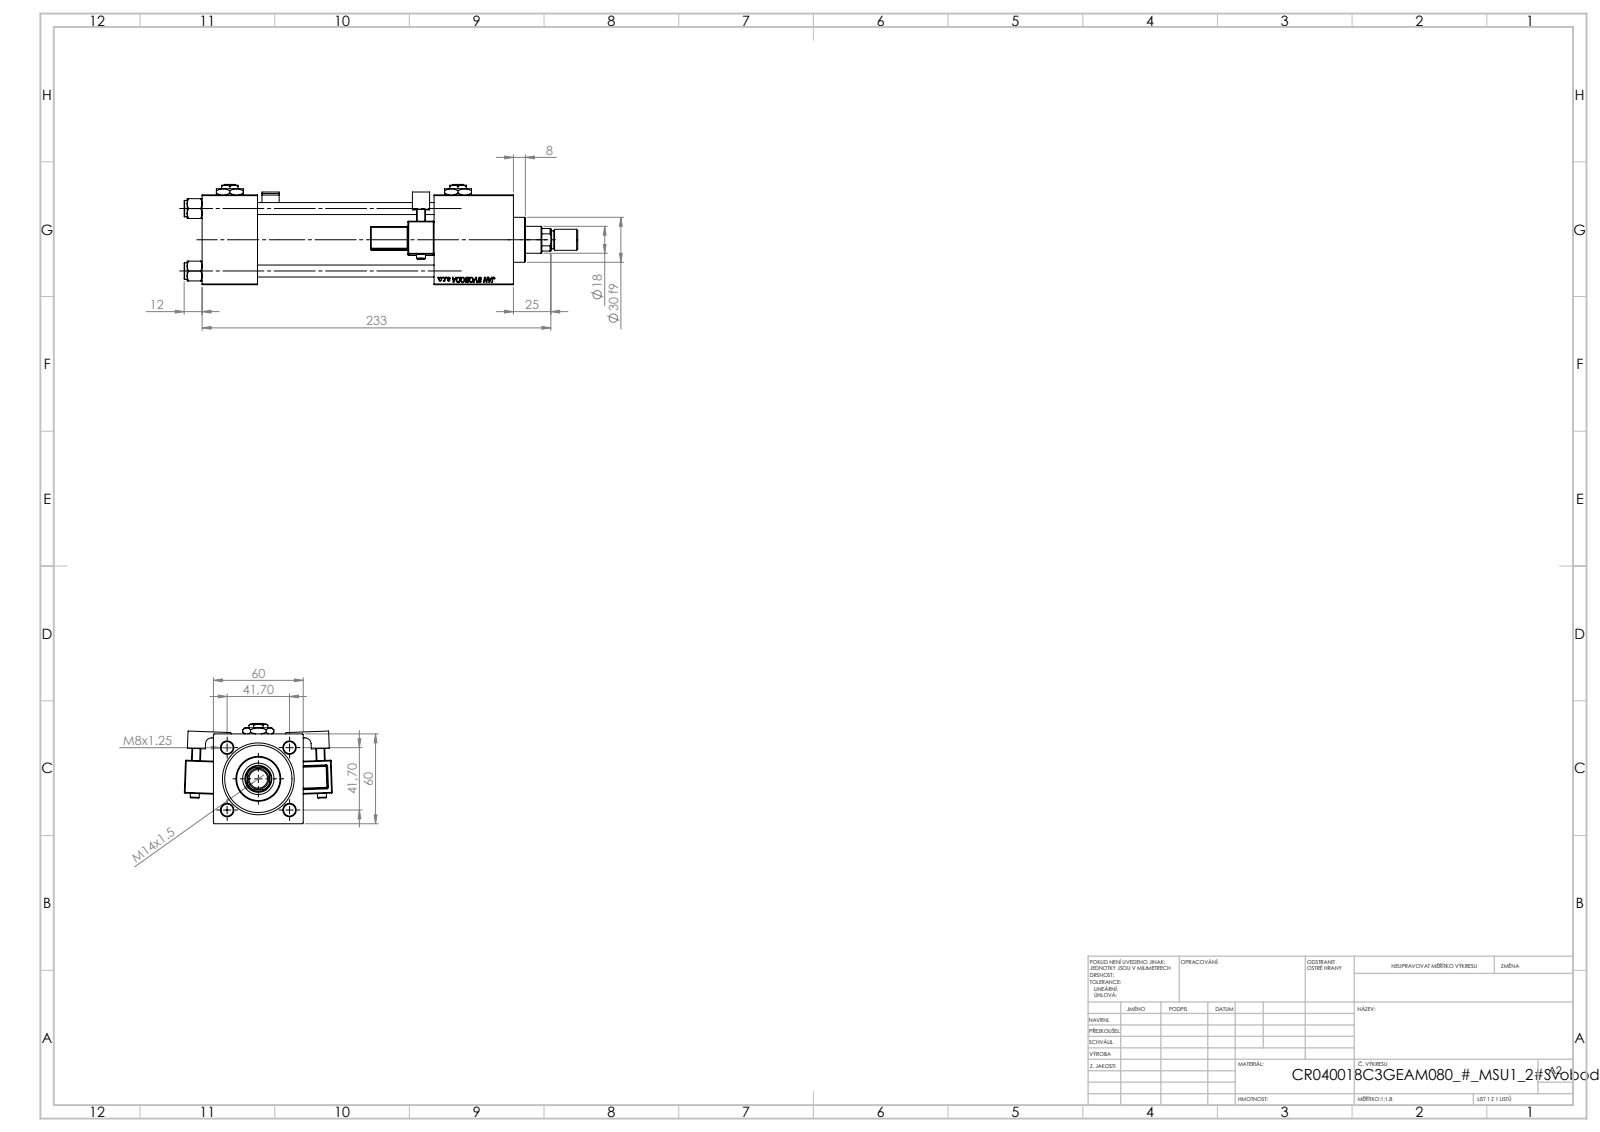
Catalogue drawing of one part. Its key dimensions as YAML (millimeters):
part_name: "ROD_END_AH; V215CR_MSU; V215_VC_A; V215CR_C_TYCINKA (+4 more)"
step_written_by: "SolidWorks 2019 (CONFIG_CONTROL_DESIGN)"
units: millimeters
bodies: {solids: 16, faces: 1418, planar: 636, cylindrical: 162, other: 620}
overall_size: [263, 98.85, 67]
volume: 493997
surface_area: 147184
round_holes:
  - {diameter: 8, count: 4}
  - {diameter: 7, count: 2}
  - {diameter: 16.66, count: 2}
  - {diameter: 24, count: 2}
  - {diameter: 8.5, count: 1}
  - {diameter: 18, count: 1}
  - {diameter: 21, count: 1}
  - {diameter: 31, count: 1}
  - {diameter: 40, count: 1}
  - {diameter: 45, count: 1}
round_bosses_or_shafts:
  - {diameter: 11, count: 4}
  - {diameter: 6, count: 2}
  - {diameter: 46, count: 1}
  - {diameter: 30, count: 1}
  - {diameter: 14, count: 1}
  - {diameter: 12, count: 1}
partial_cylinders:
  - {radius: 0.5, count: 48}
  - {radius: 1, count: 2}
  - {radius: 2.5, count: 2}
  - {radius: 4, count: 2}
  - {radius: 8.5, count: 1}
face_to_face_distances: [60, 37, 155, 118, 53, 208, 171, 179.3, 142.3, 24.3]
hole_center_spacings: [29.49, 41.7, 58.97, 152.5]
